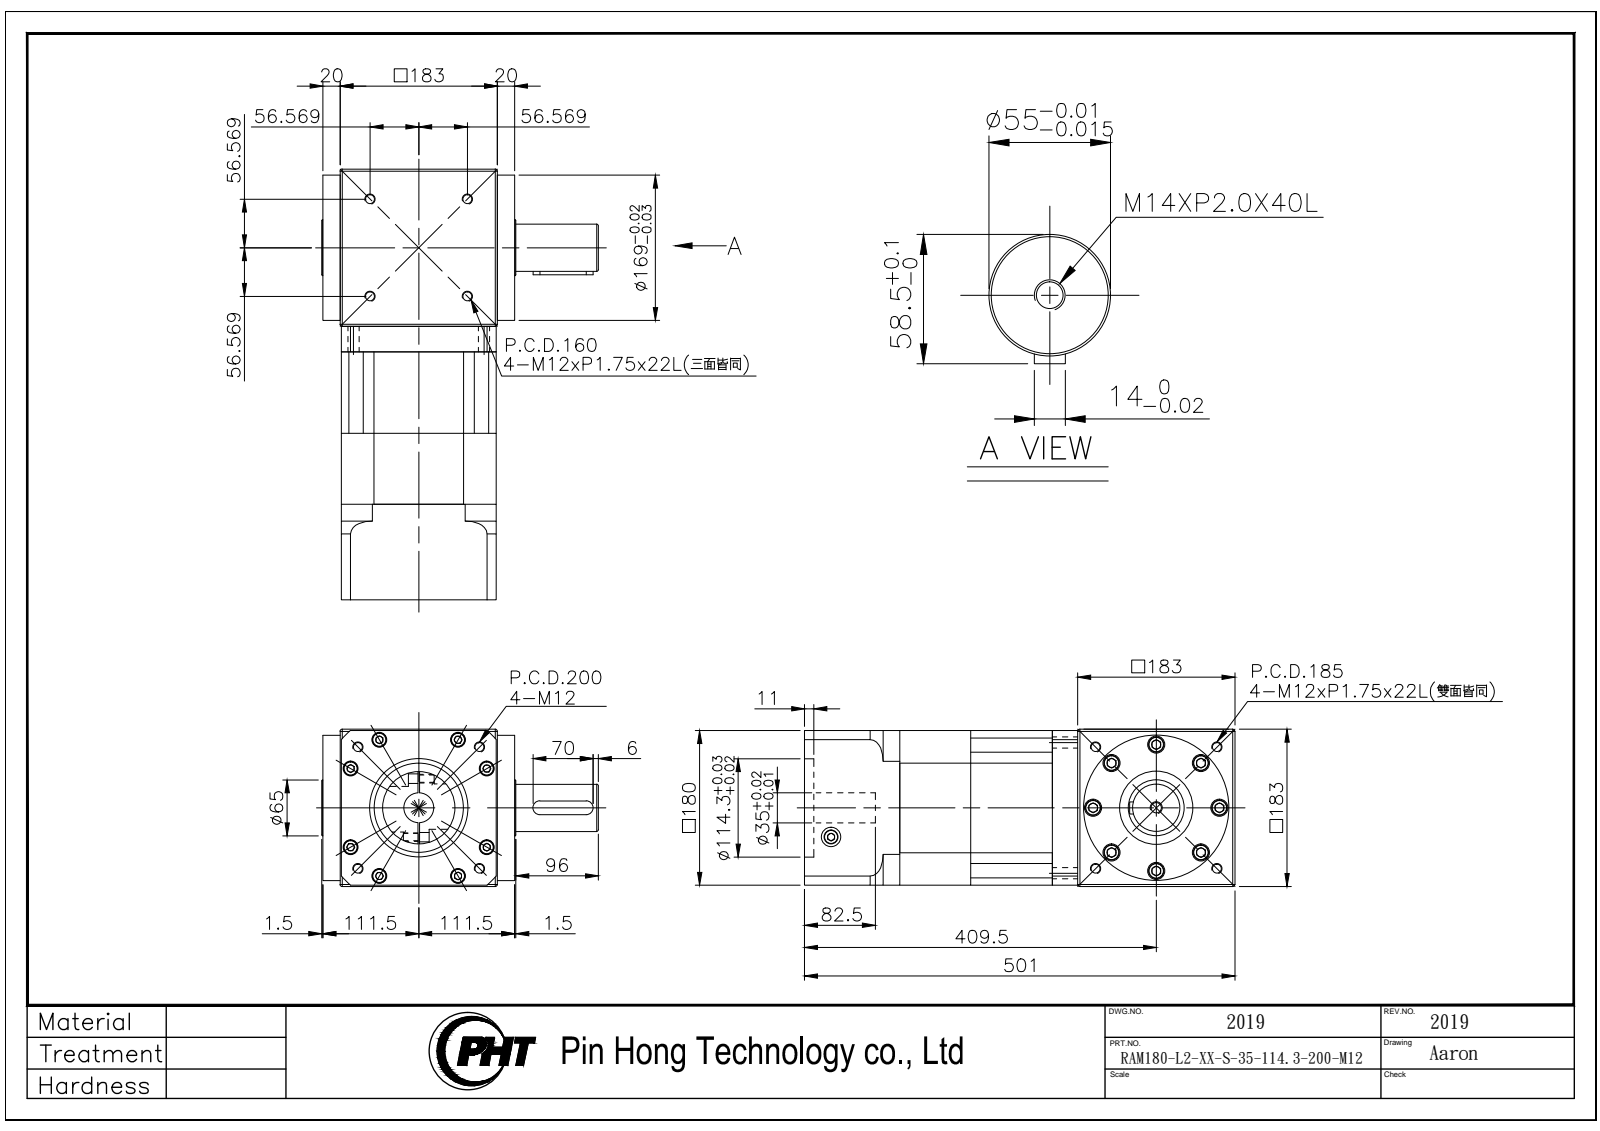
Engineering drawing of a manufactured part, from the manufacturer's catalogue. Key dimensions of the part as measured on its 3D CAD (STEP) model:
Part name (STEP PRODUCT): RAM180-L2-XX-S-35-114.3-200-M12_2019
STEP written by: SolidWorks 2016 (AUTOMOTIVE_DESIGN)
Units: millimetres
Bodies: 5 solids, 817 faces (354 planar, 285 cylindrical, 178 other)
Overall size (bounding box): 501 × 322 × 183
Volume: 16 500 000 mm³ · Surface area: 894 475 mm²
Round holes (diameter × count): ⌀10.2 ×20, ⌀11 ×8, ⌀14 ×8, ⌀17 ×8, ⌀20 ×8, ⌀13 ×4, ⌀22.5 ×2, ⌀4 ×1, ⌀12 ×1, ⌀35 ×1, ⌀104 ×1, ⌀114.3 ×1
Round bosses / shafts (diameter × count): ⌀18.3 ×8, ⌀16 ×8, ⌀18 ×4, ⌀169 ×1, ⌀160 ×1, ⌀85 ×1, ⌀84 ×1, ⌀65 ×1
Partial cylindrical surfaces — rounded edges, fillets, slot ends (radius × count): R12.5 ×4, R7 ×2, R104 ×1, R105 ×1, R120 ×1
Main face-to-face distances: 181.5, 1.5, 180, 183, 82.5, 177.5, 95, 207, 124.5, 29.5
Hole centre spacings: 91.5, 25.12, 26.38, 30.43, 56.25, 65.91, 73.5, 103.94
